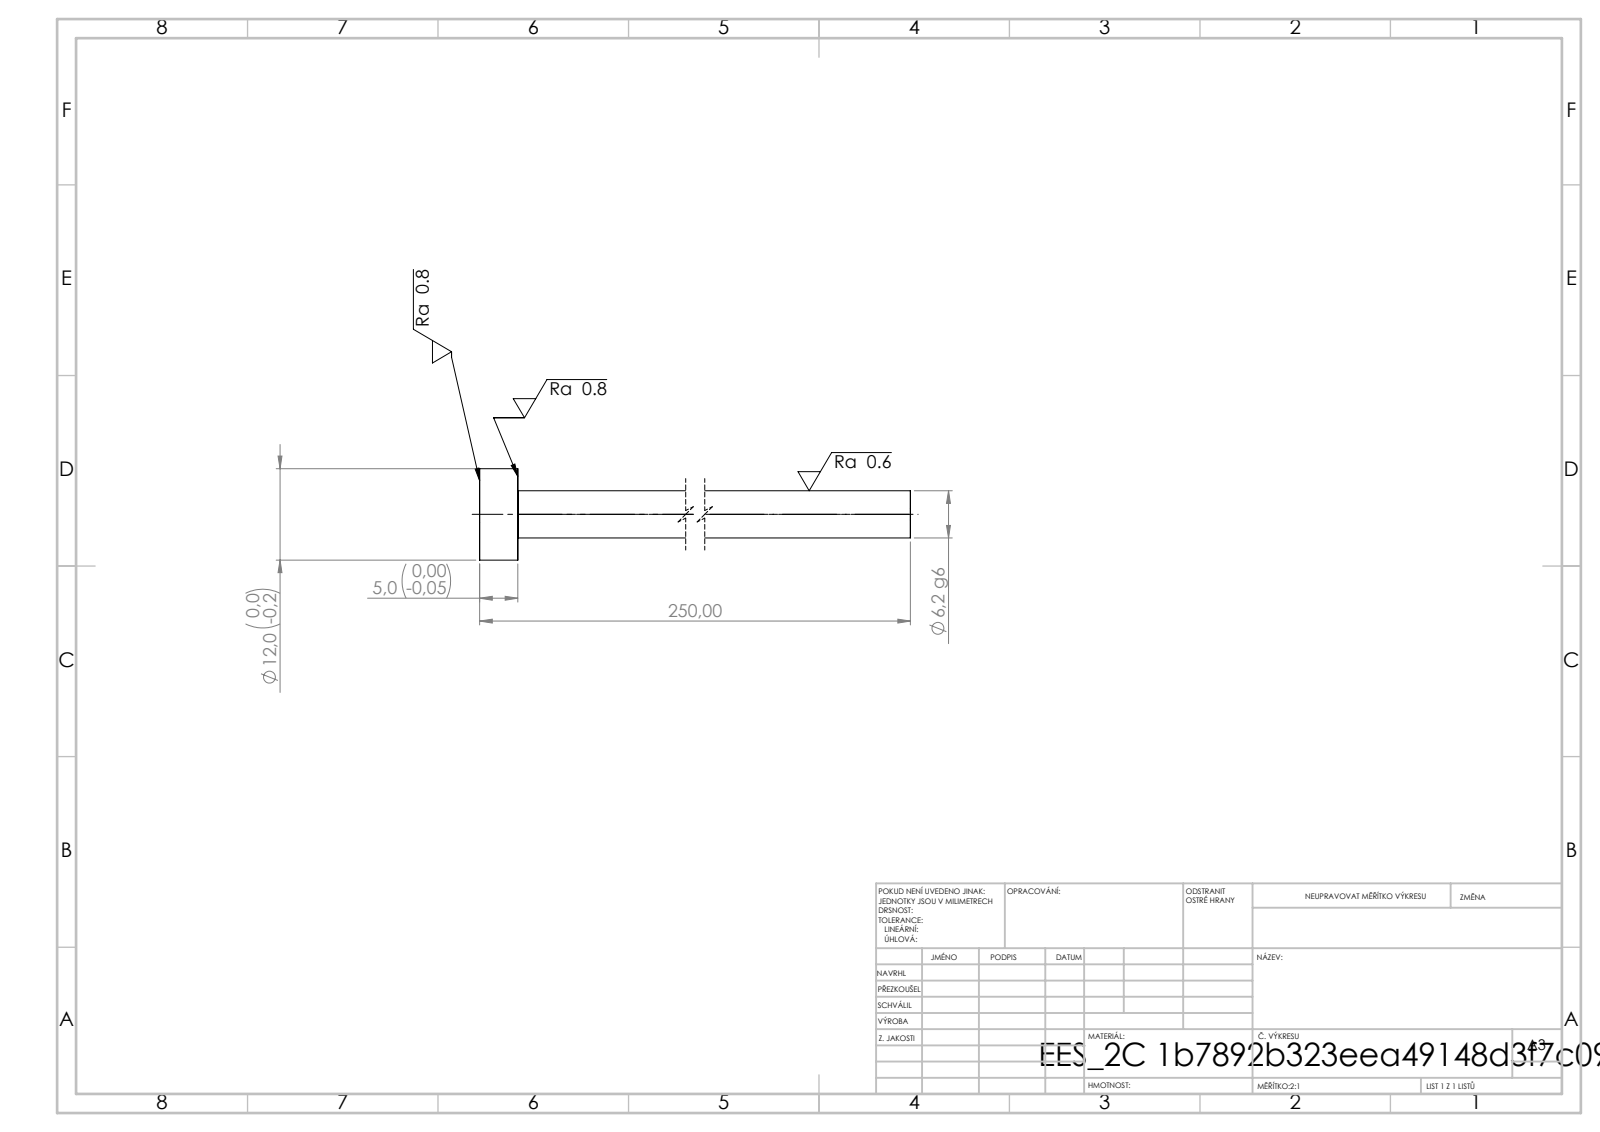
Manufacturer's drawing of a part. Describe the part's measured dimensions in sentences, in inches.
Its 3-D file was written by "SolidWorks 2019 (CONFIG_CONTROL_DESIGN)". It is 1 solid with 7 faces: 3 planar, 4 cylindrical and 0 other. Overall it measures 9.843 by 0.472 by 0.472 inches. Its volume is 0.486 cubic inches and its surface area 8.04 square inches. Round bosses or shafts: 1 of diameter 0.472, 1 of diameter 0.244. The main face-to-face distances are 0.197, 9.843, 9.646.
